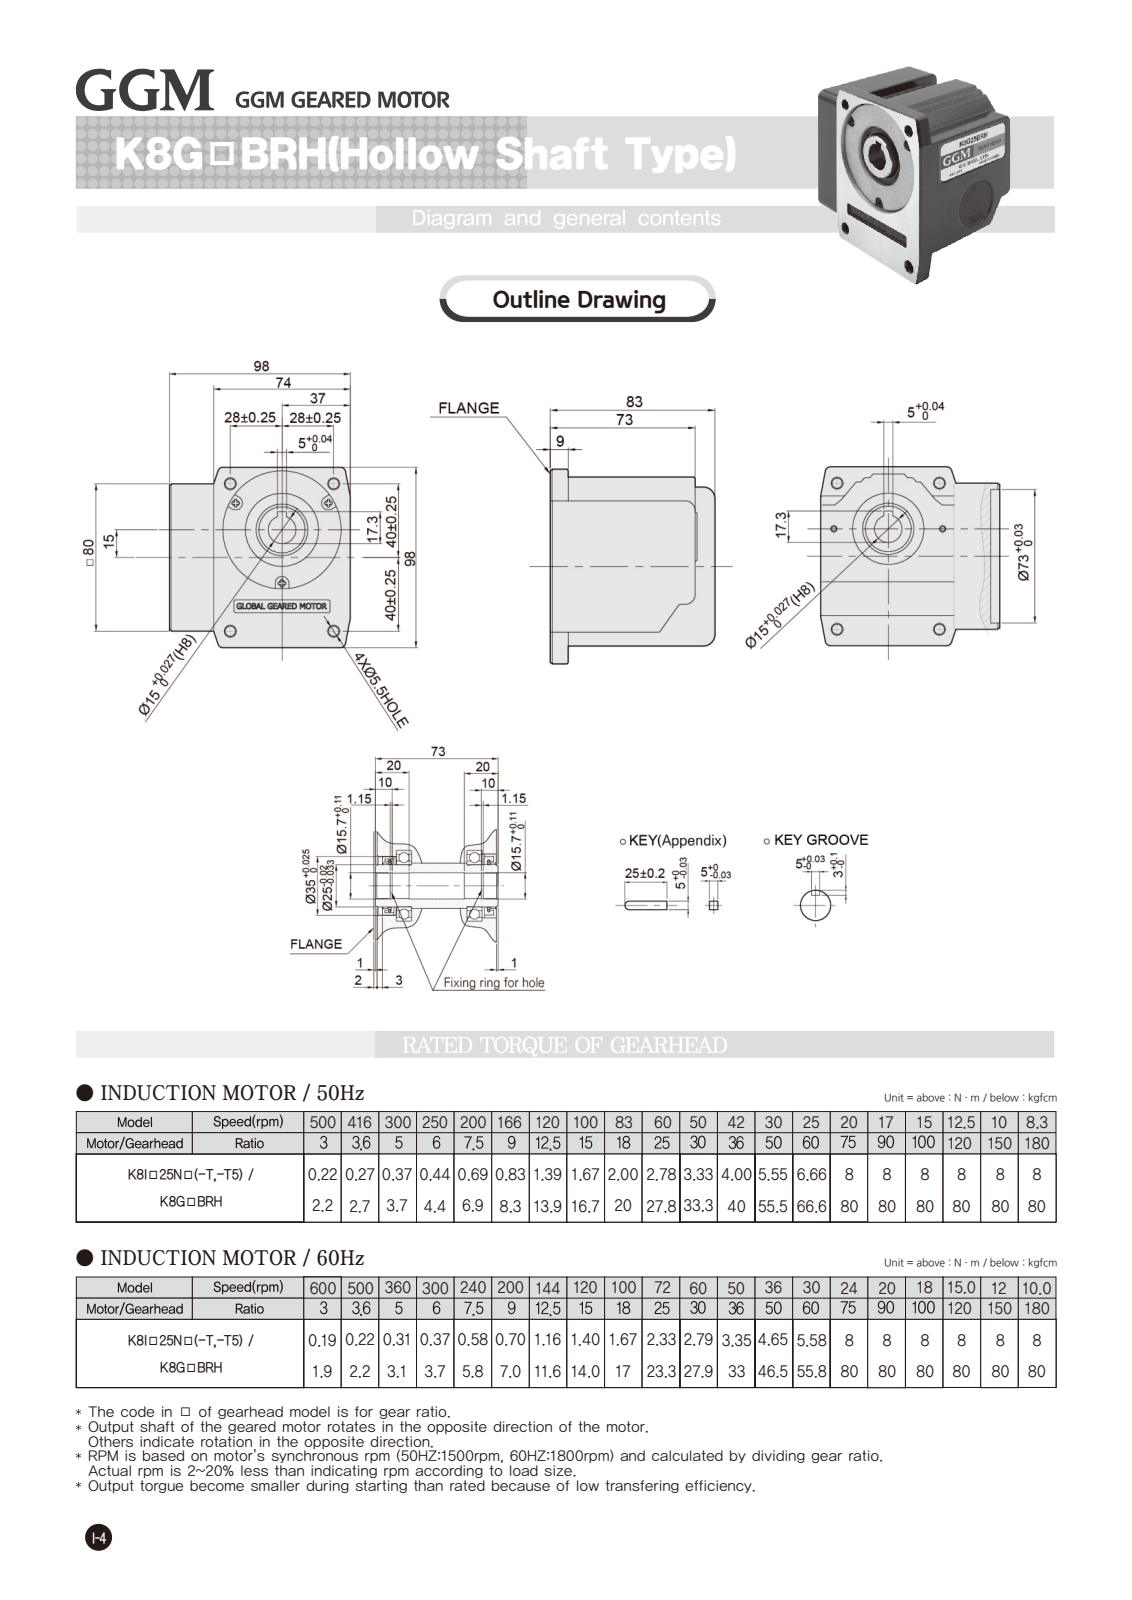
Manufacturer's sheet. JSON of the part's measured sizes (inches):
{"part_name": "K8G□BRH", "step_written_by": "Autodesk Inventor 2012 (AUTOMOTIVE_DESIGN)", "units": "inches", "bodies": {"solids": 1, "faces": 419, "planar": 167, "cylindrical": 146, "other": 106}, "overall_size": [3.858, 3.858, 3.268], "volume_in3": 30.35, "surface_area_in2": 97.5, "round_holes": [[0.217, 7], [0.098, 4], [0.138, 4], [0.165, 4], [0.059, 1], [0.197, 1], [0.394, 1], [0.417, 1], [0.433, 1], [0.512, 1], [0.591, 1], [1.063, 1]], "round_bosses_or_shafts": [[2.52, 1], [1.929, 1], [1.142, 1], [1.102, 1], [0.984, 1], [0.591, 1], [0.287, 1], [0.276, 1]], "partial_cylinders_radius": [[0.039, 41], [0.02, 16], [0.098, 4], [0.118, 4], [0.217, 4], [0.236, 4], [0.126, 3], [0.197, 2]], "face_to_face_distances": [2.874, 0.276, 0.197, 0.039, 0.079, 3.661, 3.15, 0.354, 0.118, 2.795], "hole_center_spacings": [1.26, 1.85, 2.617, 0.987, 1.142, 0.429, 0.599, 0.659]}
